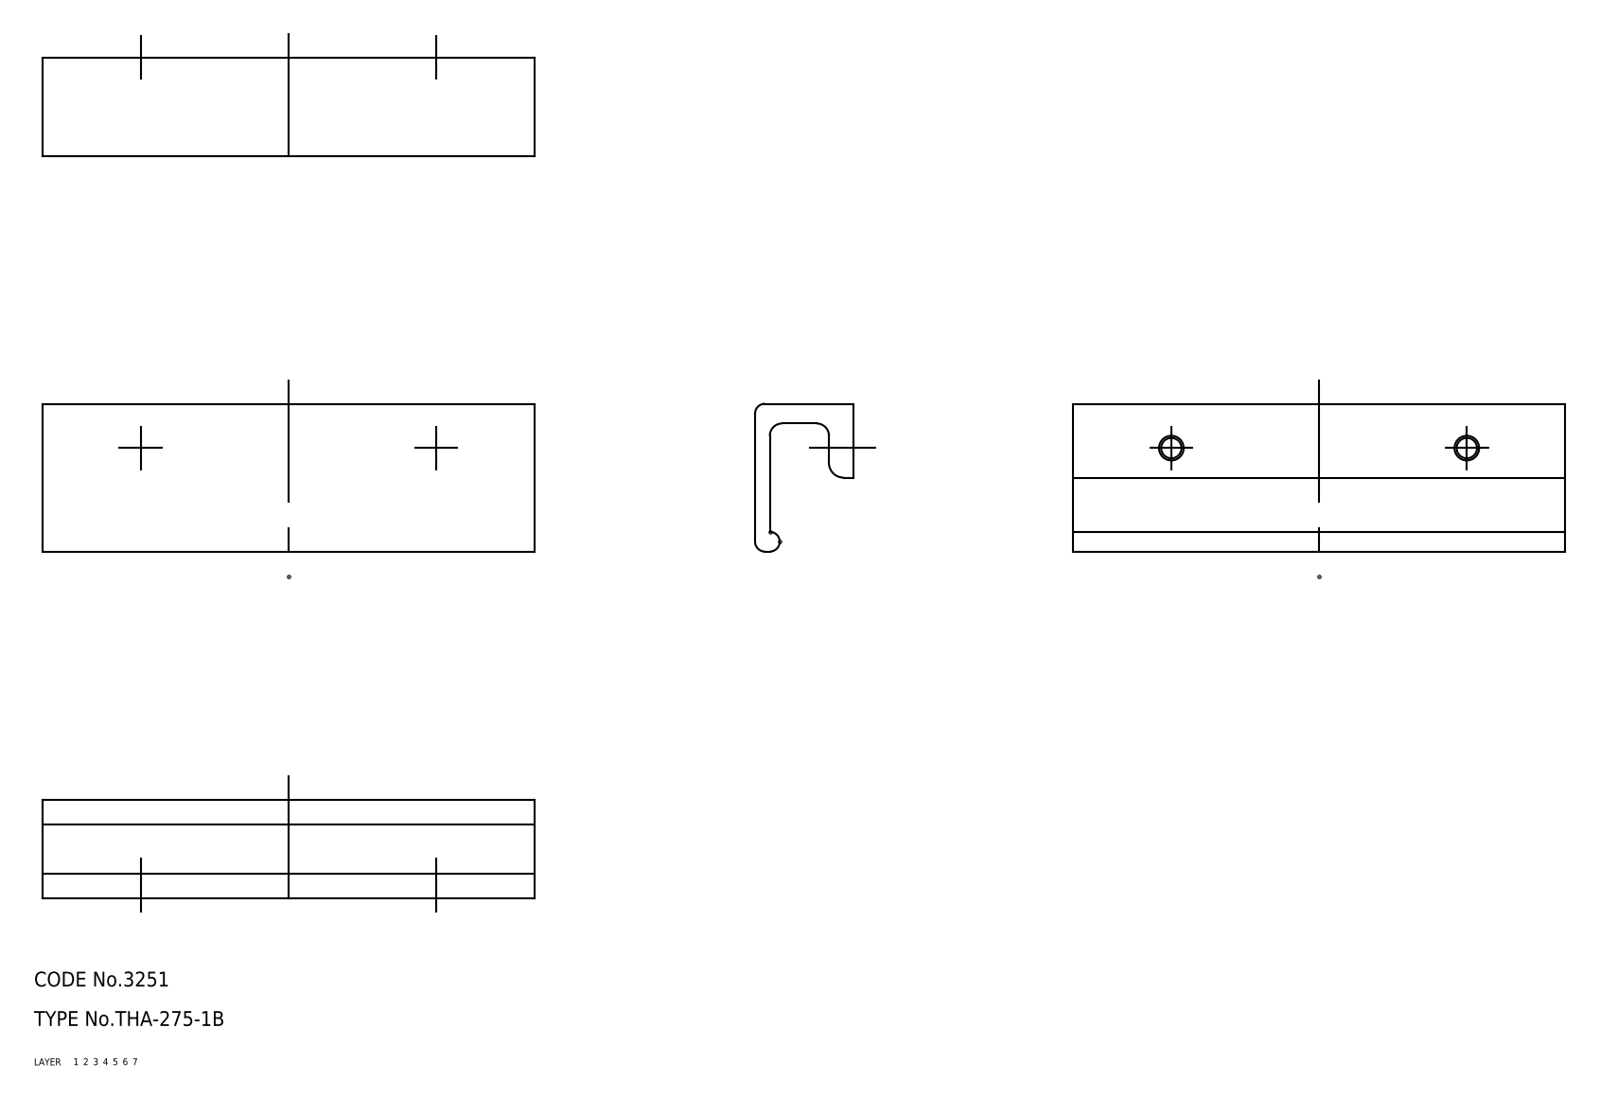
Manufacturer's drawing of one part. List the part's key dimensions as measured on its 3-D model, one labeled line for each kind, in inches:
Part name (STEP PRODUCT): pull
STEP written by: CADfix (AUTOMOTIVE_DESIGN)
Units: inches
Bodies: 1 solid, 20 faces (0 planar, 0 cylindrical, 20 other)
Overall size (bounding box): 3.937 × 1.181 × 0.787
Volume: 1.32 in³ · Surface area: 19.26 in²
